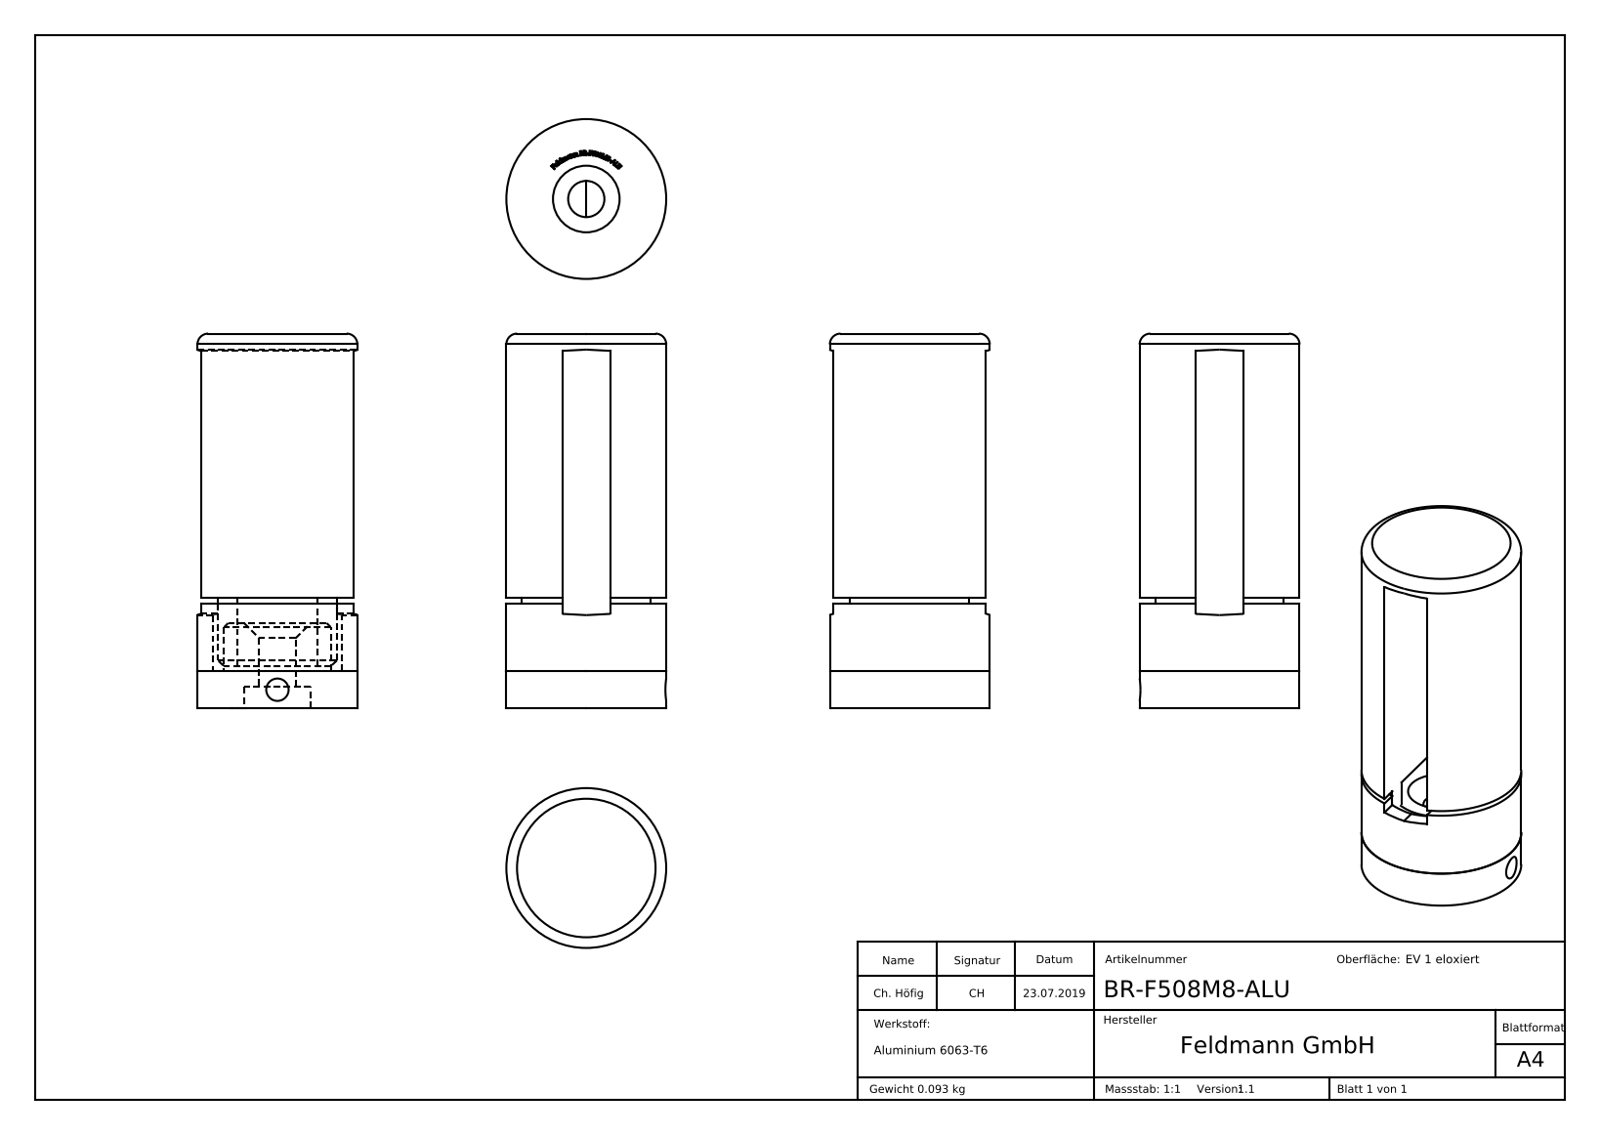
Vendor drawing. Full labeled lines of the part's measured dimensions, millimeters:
Part name (STEP PRODUCT): BR-R1XM8-XXX Teil3; BR-R1XM8-XXX Teil2; BR-R1XM8-XXX Teil2_BR-F508M8-ALU Teil2; BR-F508M8-ALU (+3 more)
STEP written by: SolidWorks 2015 (CONFIG_CONTROL_DESIGN)
Units: millimetres
Bodies: 3 solids, 329 faces (195 planar, 12 cylindrical, 122 other)
Overall size (bounding box): 70.34 × 30 × 30
Volume: 34 261 mm³ · Surface area: 14 739 mm²
Round holes (diameter × count): ⌀4.2 ×1, ⌀6.8 ×1, ⌀12.5 ×1, ⌀24.2 ×1
Round bosses / shafts (diameter × count): ⌀30 ×1, ⌀20 ×1
Partial cylindrical surfaces — rounded edges, fillets, slot ends (radius × count): R8.75 ×1, R12.05 ×1
Main face-to-face distances: 9, 7, 70.34, 63.34, 1, 12.69, 20.69, 13.69, 49.65, 8
